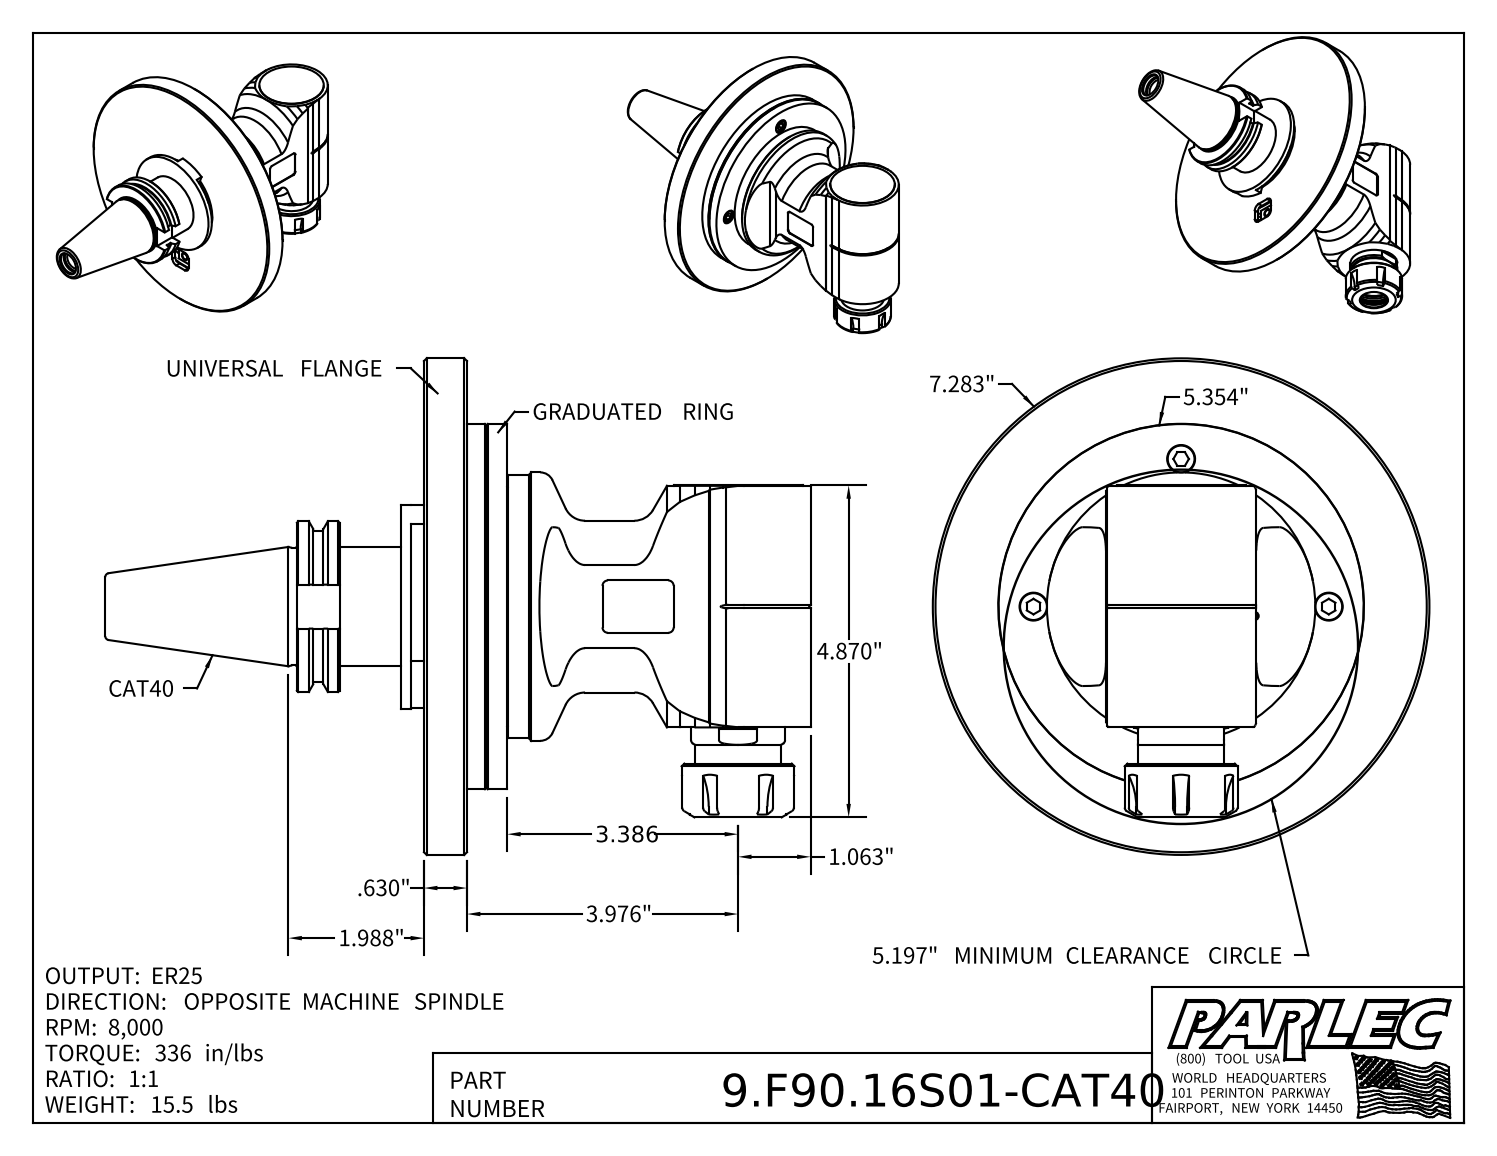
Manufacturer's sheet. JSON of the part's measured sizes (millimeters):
{"part_name": "9.F90.16S01-CAT40; 9_F90_16S01; 9_SK_44_2 (E", "step_written_by": "Autodesk Inventor 2025 (AUTOMOTIVE_DESIGN)", "units": "millimeters", "bodies": {"solids": 12, "faces": 481, "planar": 247, "cylindrical": 108, "other": 126}, "overall_size": [262.7, 185, 185], "volume_mm3": 1292000, "surface_area_mm2": 206500, "round_holes": [[10.4, 8], [5, 4], [6.4, 4], [8.5, 1], [9.5, 1], [13.4, 1], [16.3, 1], [16.8, 1], [18, 1], [20, 1], [21, 1], [23, 1]], "round_bosses_or_shafts": [[10, 8], [6, 8], [2.5, 2], [185, 1], [136.2, 1], [136, 1], [126, 1], [101.4, 1]], "partial_cylinders_radius": [[2, 12], [4, 6], [25, 6], [0.4, 2], [23, 1], [27, 1], [32, 1]], "face_to_face_distances": [16, 15, 31, 13, 3, 28, 8.5, 11.5, 21, 8], "hole_center_spacings": [38.9, 86.2, 38, 53.7, 55, 77.8, 76, 110]}
